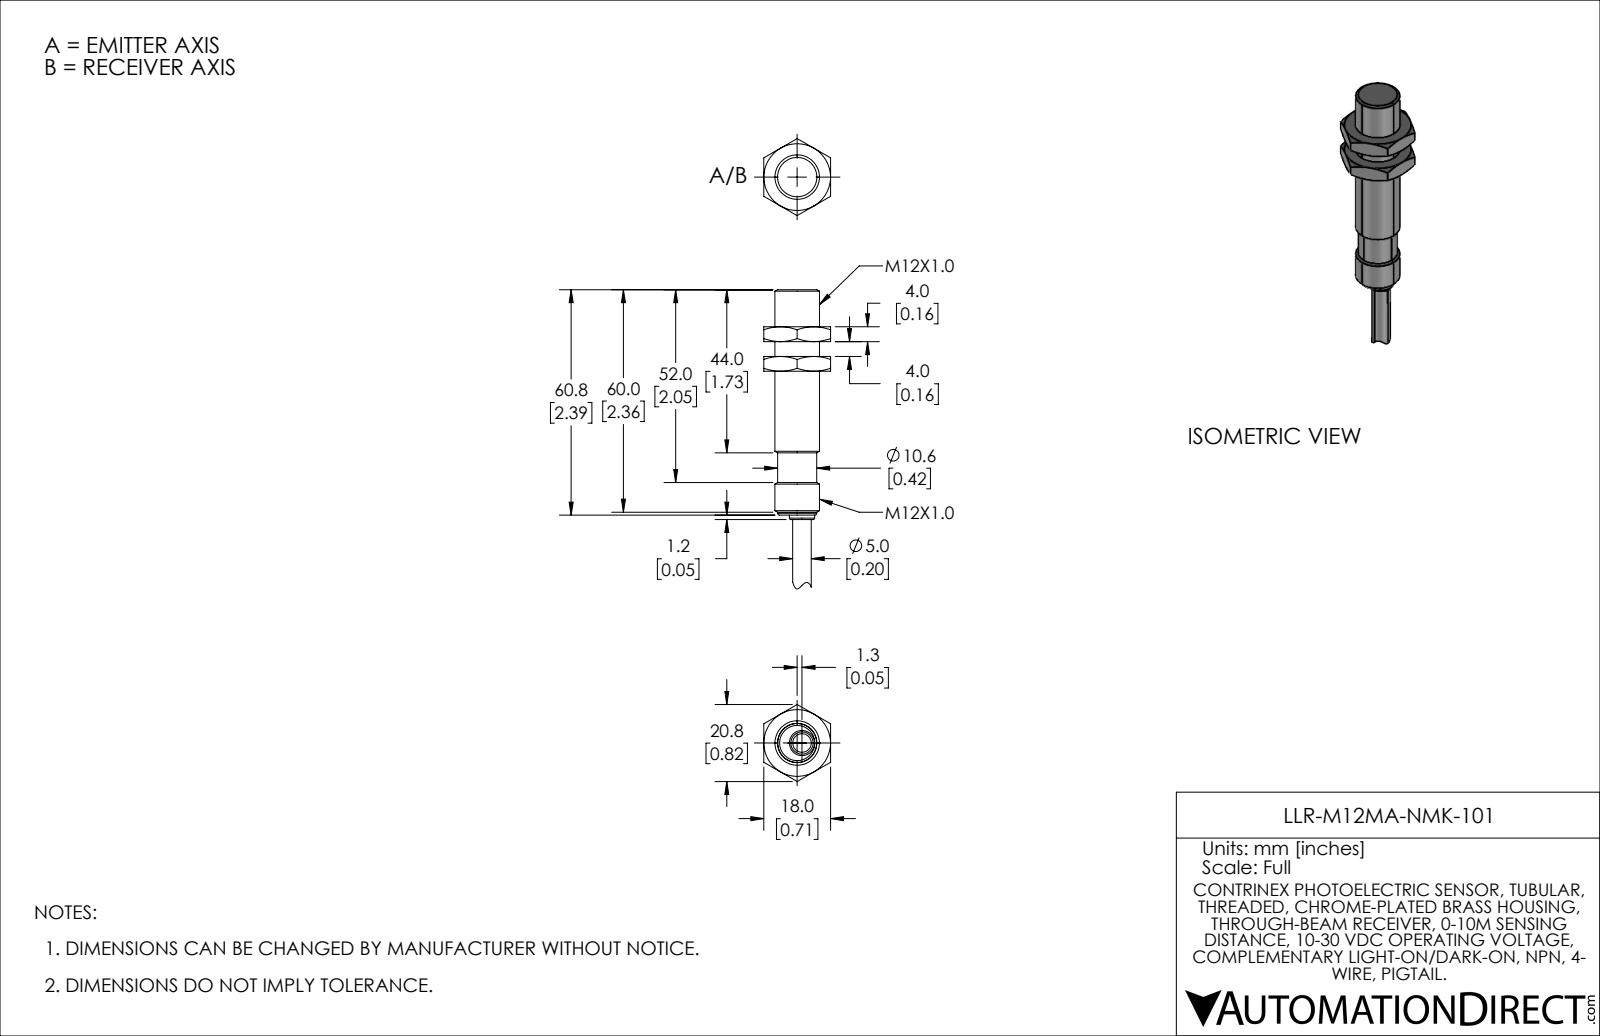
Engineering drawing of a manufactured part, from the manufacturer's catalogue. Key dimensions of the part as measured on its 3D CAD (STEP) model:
Part name (STEP PRODUCT): LLR-M12MA-NMK-101
STEP written by: SolidWorks 2021 (AUTOMOTIVE_DESIGN)
Units: inches
Bodies: 3 solids, 95 faces (20 planar, 25 cylindrical, 50 other)
Overall size (bounding box): 3.177 × 0.818 × 0.709
Volume: 0.57 in³ · Surface area: 7.139 in²
Round holes (diameter × count): ⌀0.402 ×1
Round bosses / shafts (diameter × count): ⌀0.472 ×1, ⌀0.415 ×1, ⌀0.413 ×1, ⌀0.268 ×1, ⌀0.197 ×1
Main face-to-face distances: 0.709, 0.394, 0.236, 0.63, 0.157, 1.22, 0.591, 0.827, 0.984, 2.394
